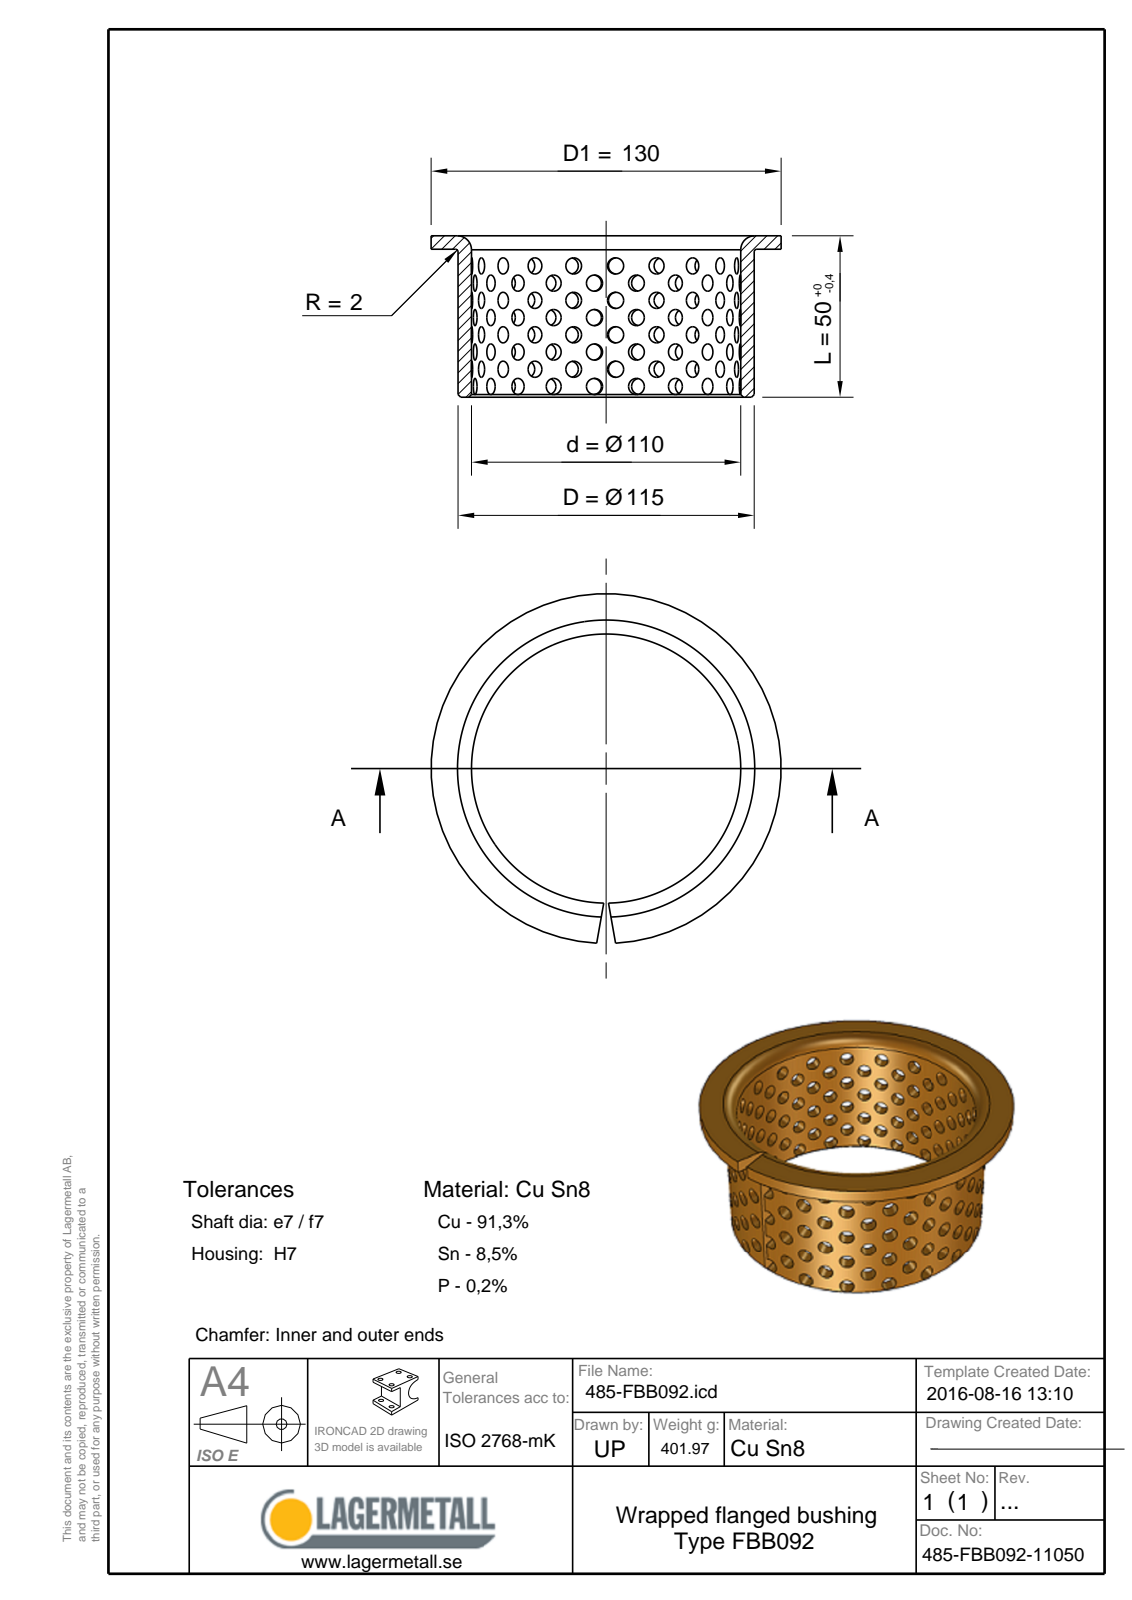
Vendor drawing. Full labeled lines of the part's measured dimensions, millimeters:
Part name (STEP PRODUCT): 485-FBB092-11050
STEP written by: Spatial InterOp 3D (CONFIG_CONTROL_DESIGN)
Units: millimetres
Bodies: 1 solid, 12 faces (5 planar, 3 cylindrical, 4 other)
Overall size (bounding box): 130 × 129.96 × 50
Volume: 49 626 mm³ · Surface area: 41 769 mm²
Round holes (diameter × count): ⌀110 ×1
Round bosses / shafts (diameter × count): ⌀130 ×1, ⌀115 ×1
Main face-to-face distances: 2.5, 47.5, 50
